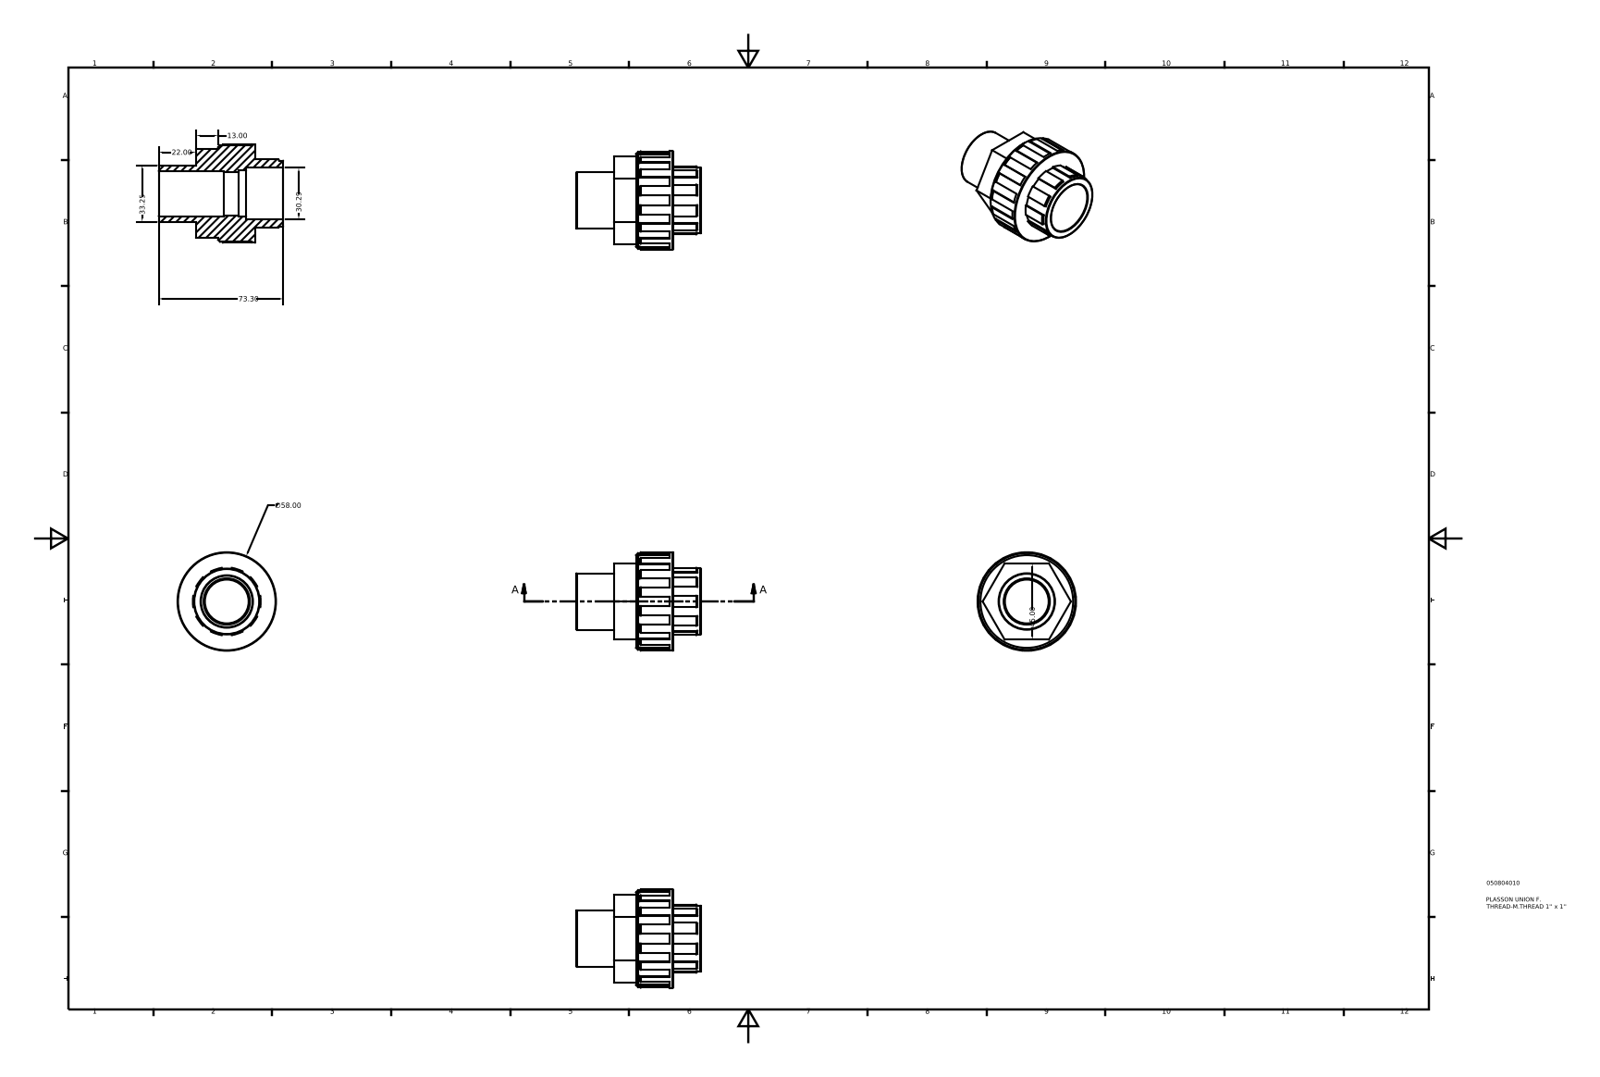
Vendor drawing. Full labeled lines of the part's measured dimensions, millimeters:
Part name (STEP PRODUCT): 050804010
STEP written by: Autodesk Inventor 2015 (AUTOMOTIVE_DESIGN)
Units: millimetres
Bodies: 1 solid, 132 faces (82 planar, 18 cylindrical, 32 other)
Overall size (bounding box): 73.3 × 58 × 58
Volume: 74 035 mm³ · Surface area: 21 142 mm²
Round holes (diameter × count): ⌀25.75 ×1, ⌀26.6 ×1, ⌀27.26 ×1, ⌀30.29 ×1
Round bosses / shafts (diameter × count): ⌀58 ×1, ⌀56.84 ×1, ⌀38.77 ×1, ⌀33.25 ×1
Partial cylindrical surfaces — rounded edges, fillets, slot ends (radius × count): R19.99 ×1
Main face-to-face distances: 45, 34.8, 13, 21.8, 51.3, 16.5, 38.3, 22, 35, 56.8
